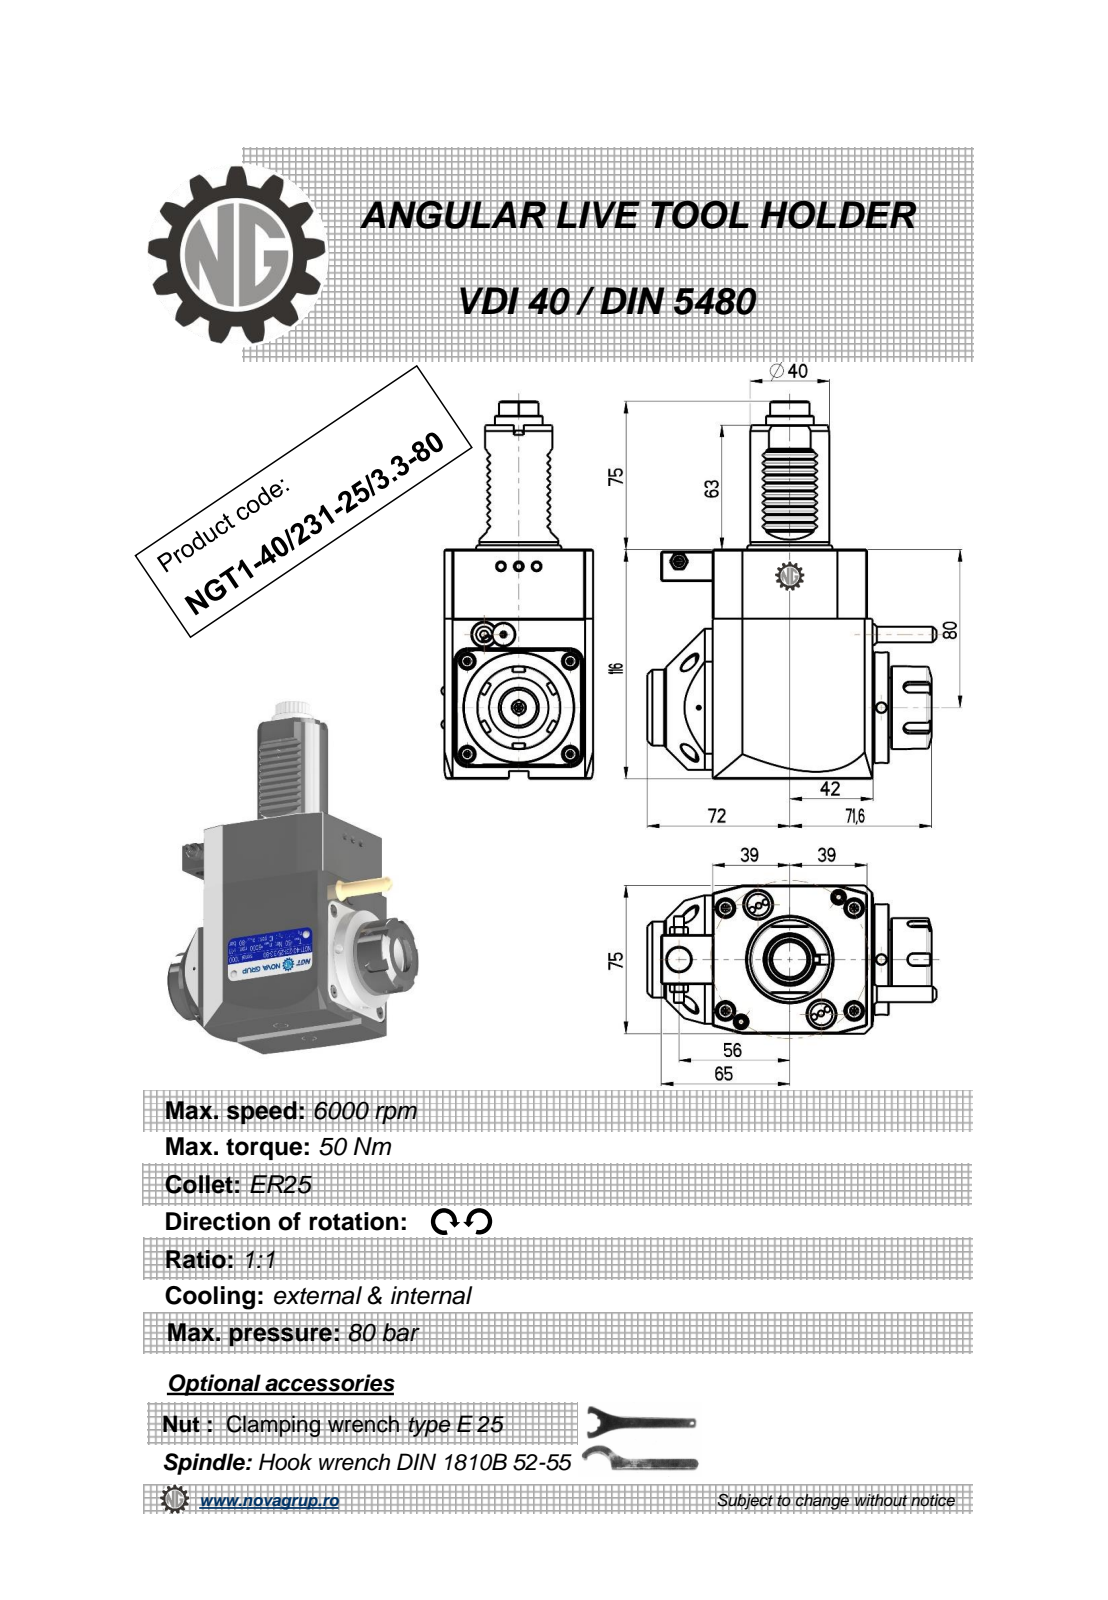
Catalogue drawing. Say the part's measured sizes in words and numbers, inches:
The part is named "NGT1_40_231_25_3_3_80". Its 3-D file was written by "PRO/ENGINEER BY PARAMETRIC TECHNOLOGY CORPORATION, 2010280 (CONFIG_CONTROL_DESIGN)". It is 1 solid with 599 faces: 229 planar, 193 cylindrical and 177 other. Overall it measures 7.52 by 5.754 by 2.953 inches. Its volume is 54.5 cubic inches and its surface area 112.3 square inches. Round holes: 3 of diameter 0.197, 1 of diameter 0.118, 1 of diameter 0.165, 1 of diameter 0.374, 1 of diameter 0.472, 1 of diameter 0.799. Round bosses or shafts: 1 of diameter 2.205, 1 of diameter 1.693, 1 of diameter 1.654, 1 of diameter 1.575, 1 of diameter 1.516, 1 of diameter 1.299, 1 of diameter 0.945, 1 of diameter 0.441. Partial cylindrical surfaces (rounded edges, fillets, slot ends): 48 of radius 0.082, 20 of radius 0.012, 12 of radius 0.01, 6 of radius 0.009, 5 of radius 0.118, 1 of radius 0.357, 1 of radius 0.391, 1 of radius 0.591. The main face-to-face distances are 2.953, 4.567, 3.189, 3.071, 0.118, 0.433, 0.315, 4.37, 0.295, 0.02. The hole center spacings are 1.523, 1.611, 2.815, 4.026, 4.969.
